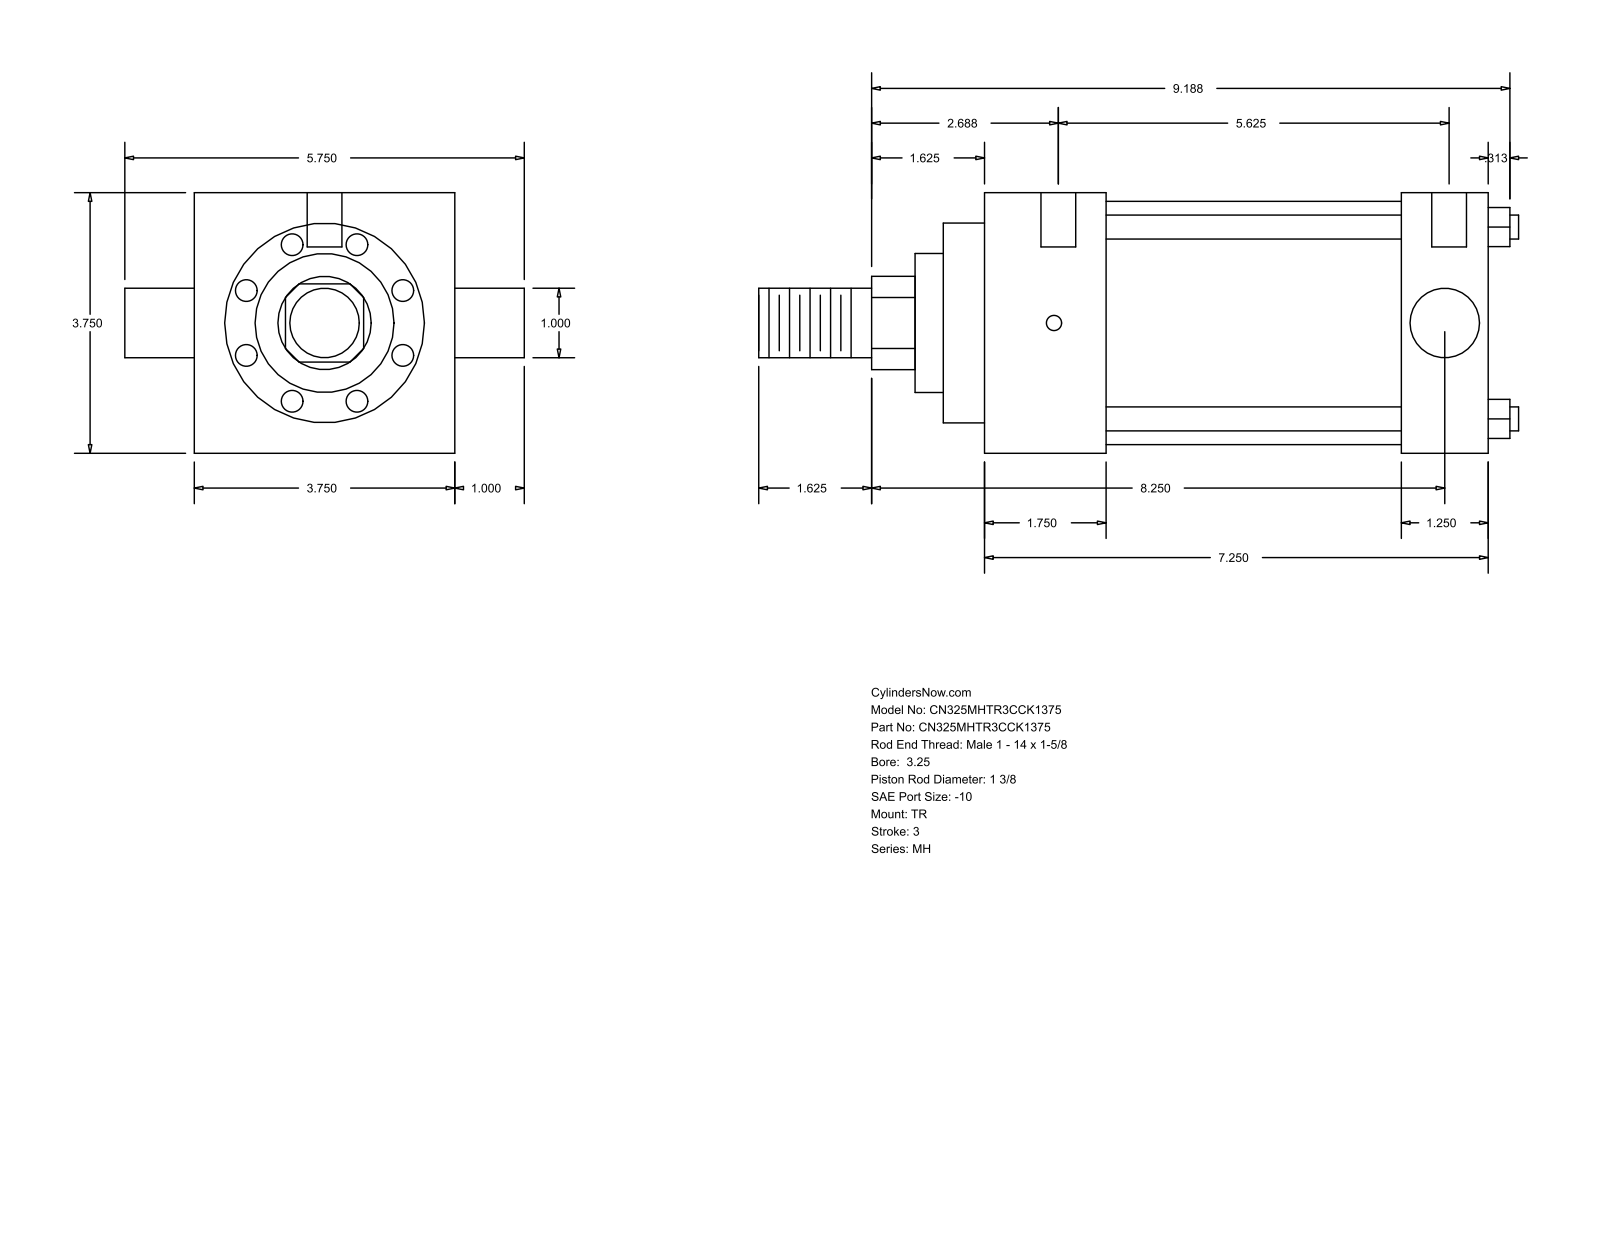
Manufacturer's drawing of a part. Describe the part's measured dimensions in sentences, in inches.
The part is named "MH_TR__0325_1.375". Its 3-D file was written by "GSSL Pune (CONFIG_CONTROL_DESIGN)". It is 0 solids with 86 faces: 61 planar, 25 cylindrical and 0 other. Overall it measures 10.937 by 5.75 by 3.75 inches. Round holes: 3 of diameter 0.219, 2 of diameter 0.5. Round bosses or shafts: 4 of diameter 0.345, 2 of diameter 1, 1 of diameter 3.5, 1 of diameter 2.875, 1 of diameter 2, 1 of diameter 1.375. Partial cylindrical surfaces (rounded edges, fillets, slot ends): 1 of radius 0.672. The main face-to-face distances are 3.75, 7.25, 1.75, 6, 4.25, 5.5, 1.25, 0.594, 2.344, 6.594. The hole center spacings are 0.063, 0.187, 5.625, 5.688, 5.813, 5.875.
